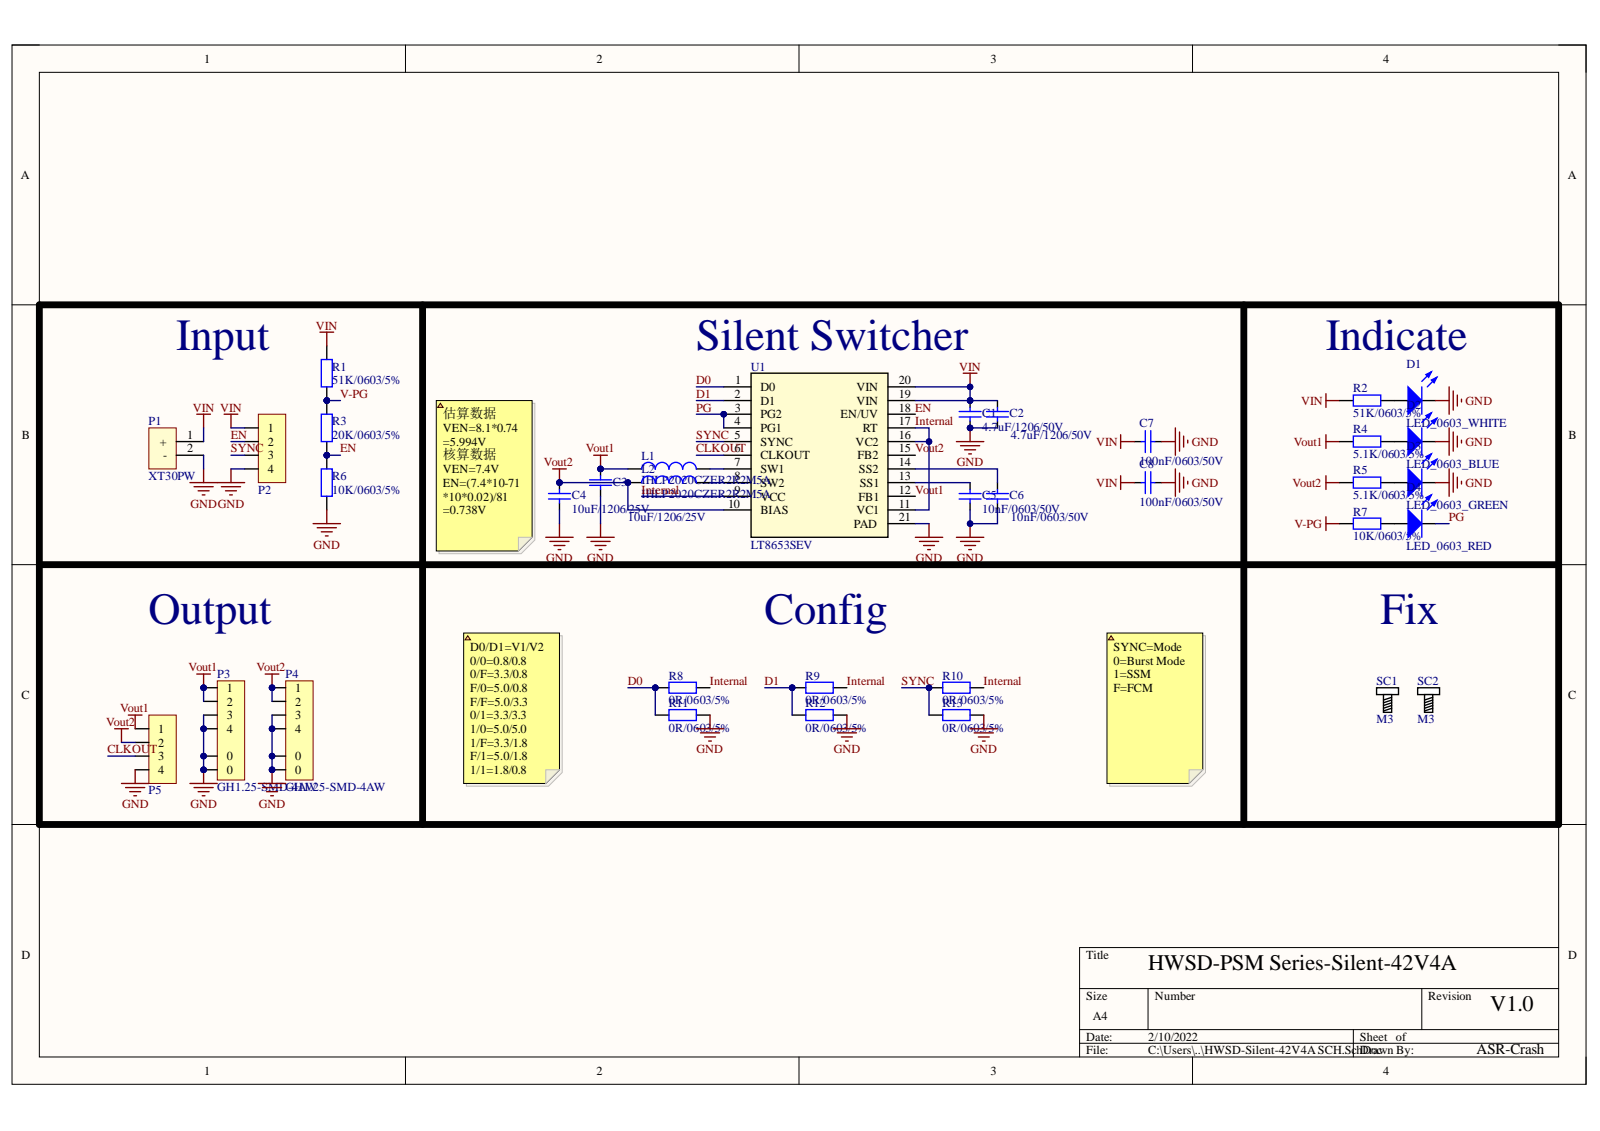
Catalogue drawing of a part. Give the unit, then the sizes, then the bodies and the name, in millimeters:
Units: millimetres
Overall size (bounding box): 40 × 20 × 13.52
Round holes (diameter × count): ⌀1 ×12, ⌀0.92 ×2, ⌀1.8 ×2, ⌀3 ×2
Round bosses / shafts (diameter × count): ⌀2 ×4, ⌀2.5 ×2, ⌀1.5 ×2, ⌀0.98 ×2, ⌀0.9 ×2
Partial cylindrical surfaces — rounded edges, fillets, slot ends (radius × count): R0.18 ×48, R0.1 ×36, R0.62 ×16, R0.13 ×8, R0.15 ×8, R0.17 ×8, R0.2 ×6, R2.54 ×4
Main face-to-face distances: 1.69, 0.6, 2.5, 5, 6.69, 4.4, 1.9, 0.97, 16.7, 2.13
Hole centre spacings: 2.54, 5.08, 16.7, 12.81, 16.89, 16.9, 7.62, 10.44
Volume: 2 194 mm³ · Surface area: 4 249 mm²
Bodies: 100 solids, 2309 faces (1554 planar, 401 cylindrical, 354 other)
Part name (STEP PRODUCT): PCB; Board; C8; User_Library-0603_SMD_Capacitor (+6 more)
STEP written by: Open CASCADE 6.8 (AUTOMOTIVE_DESIGN)
